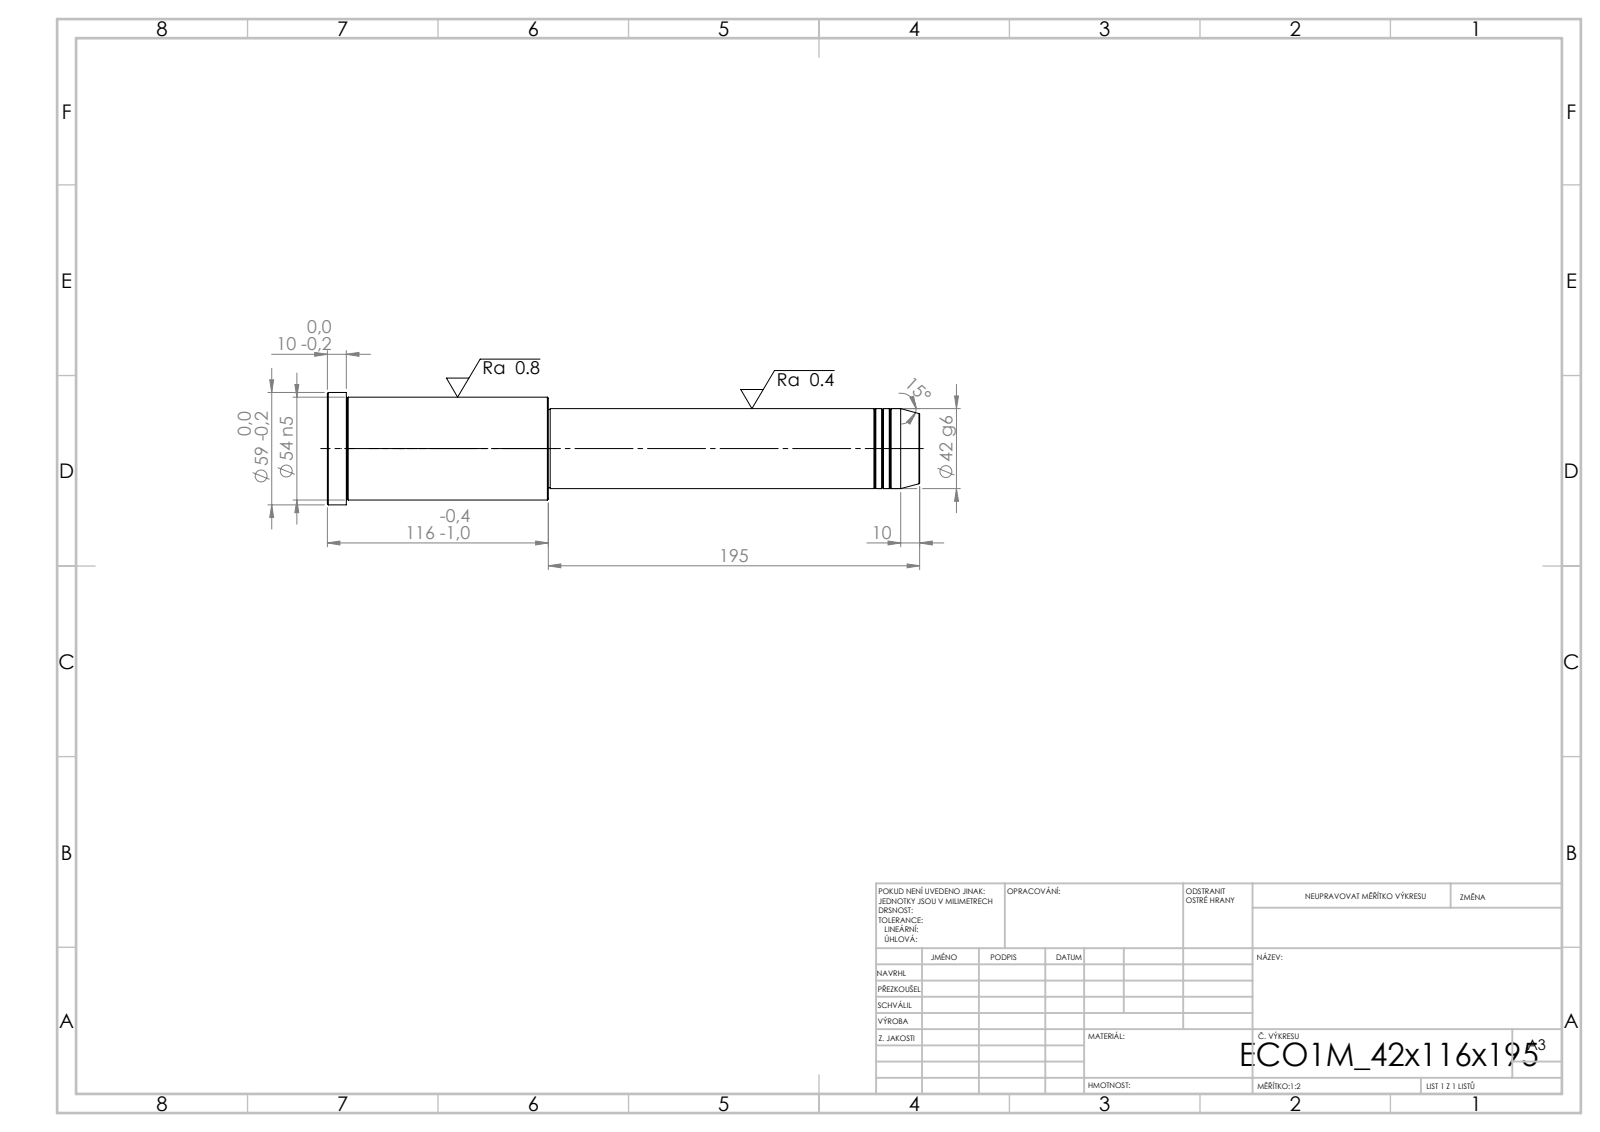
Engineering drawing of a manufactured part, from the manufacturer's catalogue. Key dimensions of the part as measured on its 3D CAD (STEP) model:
STEP written by: SolidWorks 2019 (CONFIG_CONTROL_DESIGN)
Units: millimetres
Bodies: 1 solid, 43 faces (5 planar, 14 cylindrical, 24 other)
Overall size (bounding box): 311 × 59 × 59
Volume: 538 239 mm³ · Surface area: 50 982 mm²
Round bosses / shafts (diameter × count): ⌀59 ×1, ⌀54 ×1, ⌀42 ×1, ⌀41 ×1
Main face-to-face distances: 311, 195, 116, 301, 106, 10, 194, 1, 107, 117
